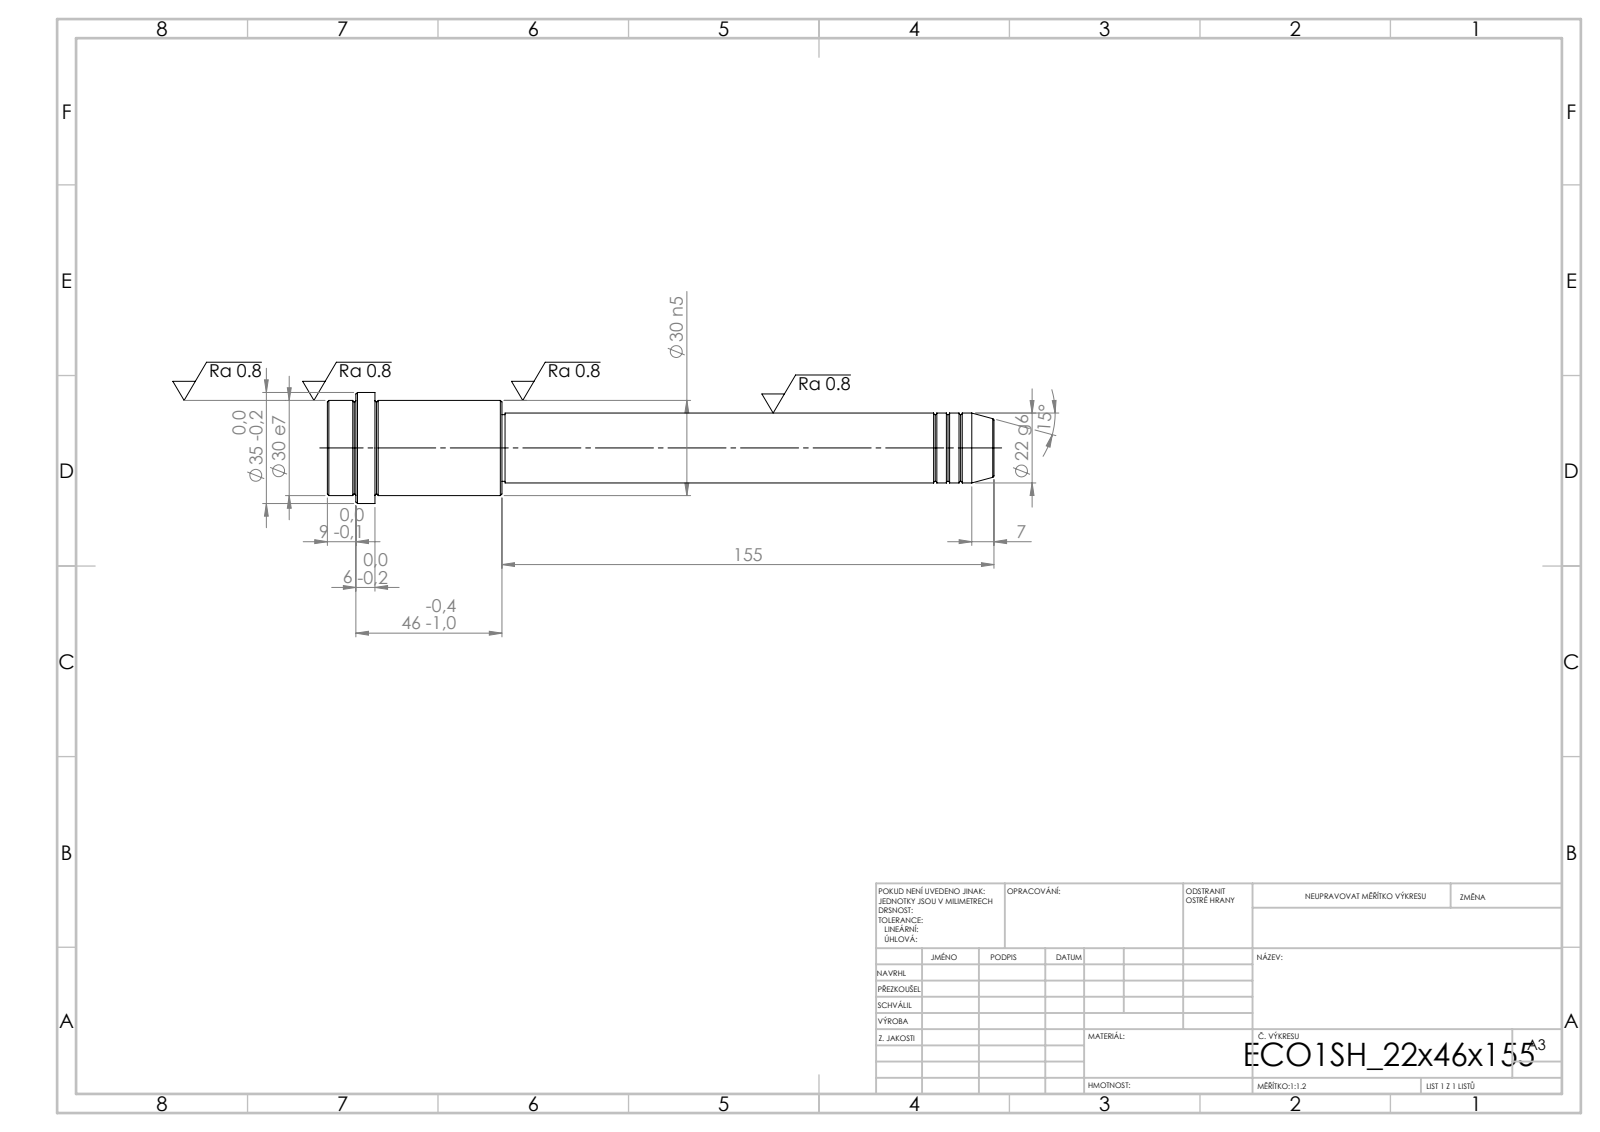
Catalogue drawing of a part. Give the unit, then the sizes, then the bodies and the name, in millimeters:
Units: millimetres
Overall size (bounding box): 210 × 35 × 35
Round bosses / shafts (diameter × count): ⌀35 ×1, ⌀30 ×1, ⌀22 ×1, ⌀21 ×1
Main face-to-face distances: 55, 40, 15, 155, 195, 210, 201, 46, 6, 9
Volume: 98 676 mm³ · Surface area: 17 950 mm²
Bodies: 1 solid, 52 faces (6 planar, 16 cylindrical, 30 other)
STEP written by: SolidWorks 2019 (CONFIG_CONTROL_DESIGN)
